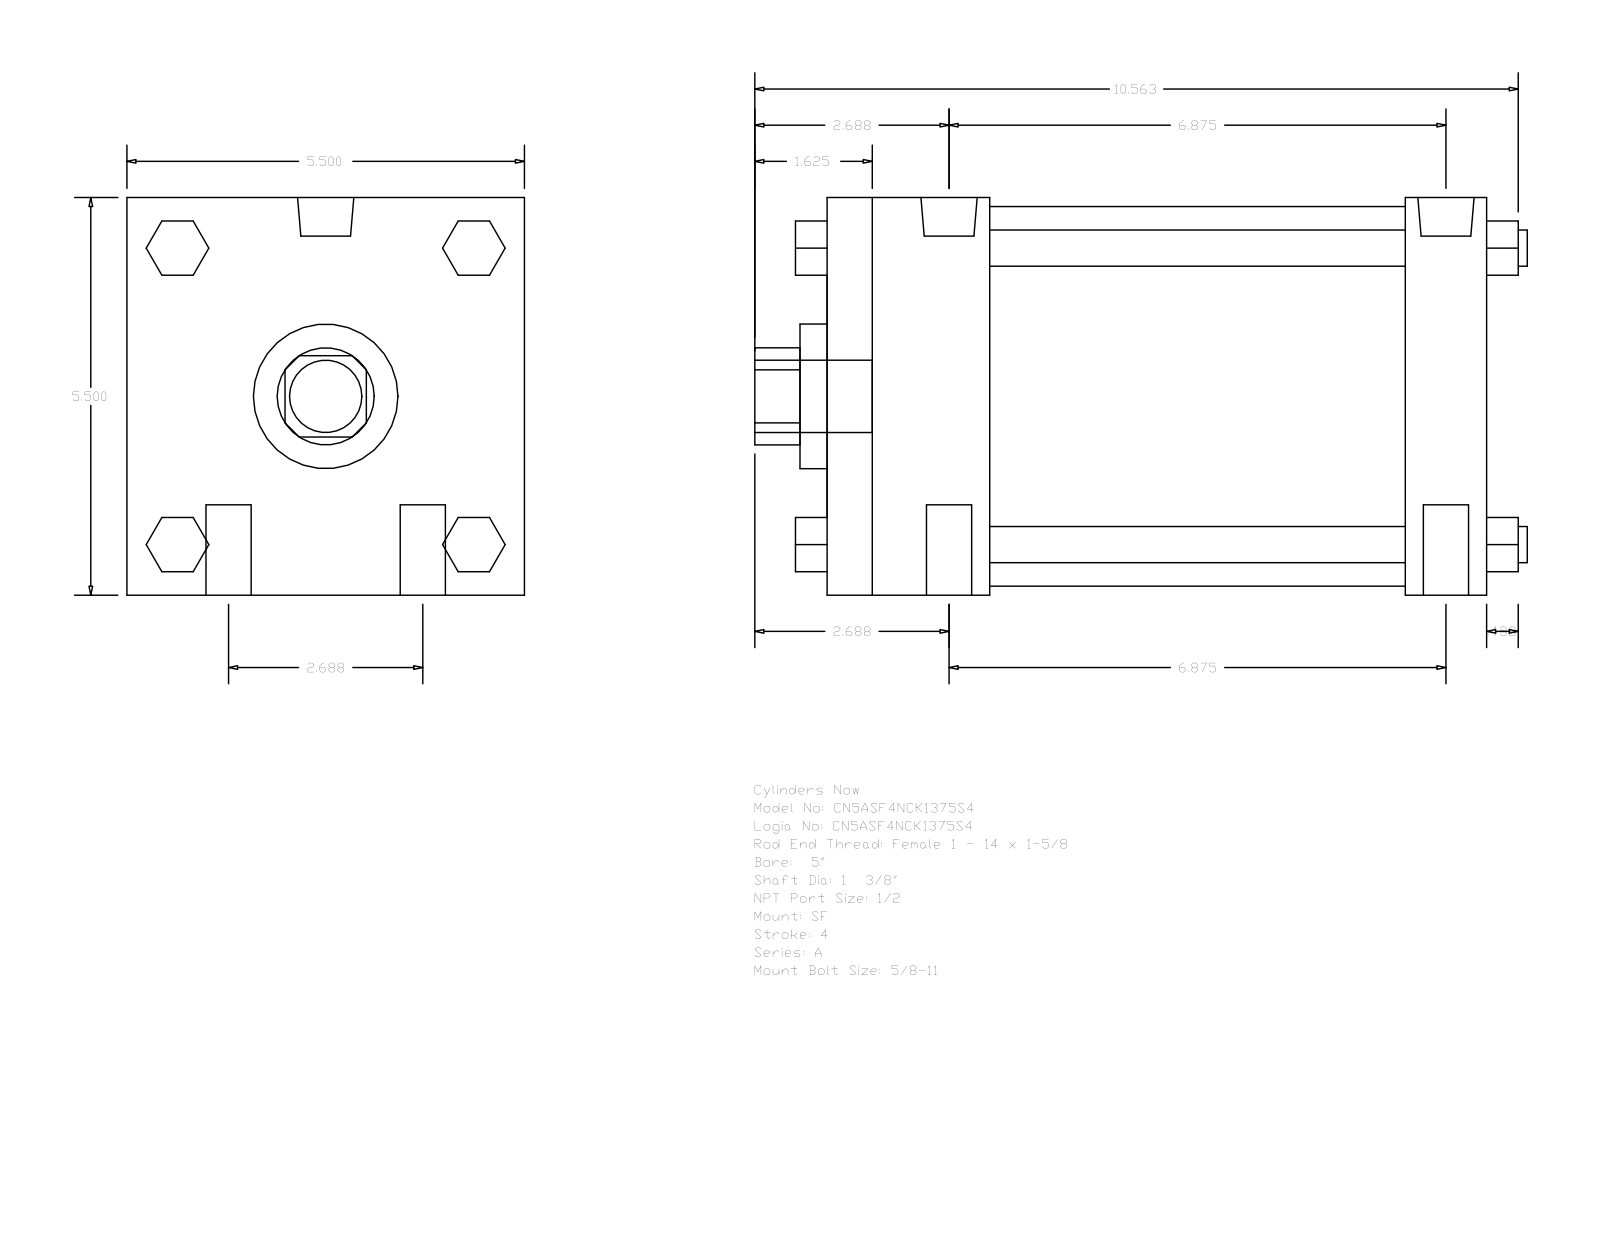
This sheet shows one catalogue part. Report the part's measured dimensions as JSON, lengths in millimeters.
{"part_name": "A_SF__0500_1.375", "step_written_by": "GSSL Pune (CONFIG_CONTROL_DESIGN)", "units": "millimeters", "bodies": {"solids": 0, "faces": 124, "planar": 94, "cylindrical": 30, "other": 0}, "overall_size": [271.46, 139.7, 139.7], "round_holes": [[34.92, 1], [50.8, 1], [133.35, 1]], "round_bosses_or_shafts": [[15.88, 4], [12.7, 4], [19.77, 2], [8.73, 2], [25.4, 1]], "partial_cylinders_radius": [[17.06, 1]], "face_to_face_distances": [139.7, 231.78, 28.58, 57.15, 203.2, 146.05, 174.63, 19.05, 52.07, 90.18]}
